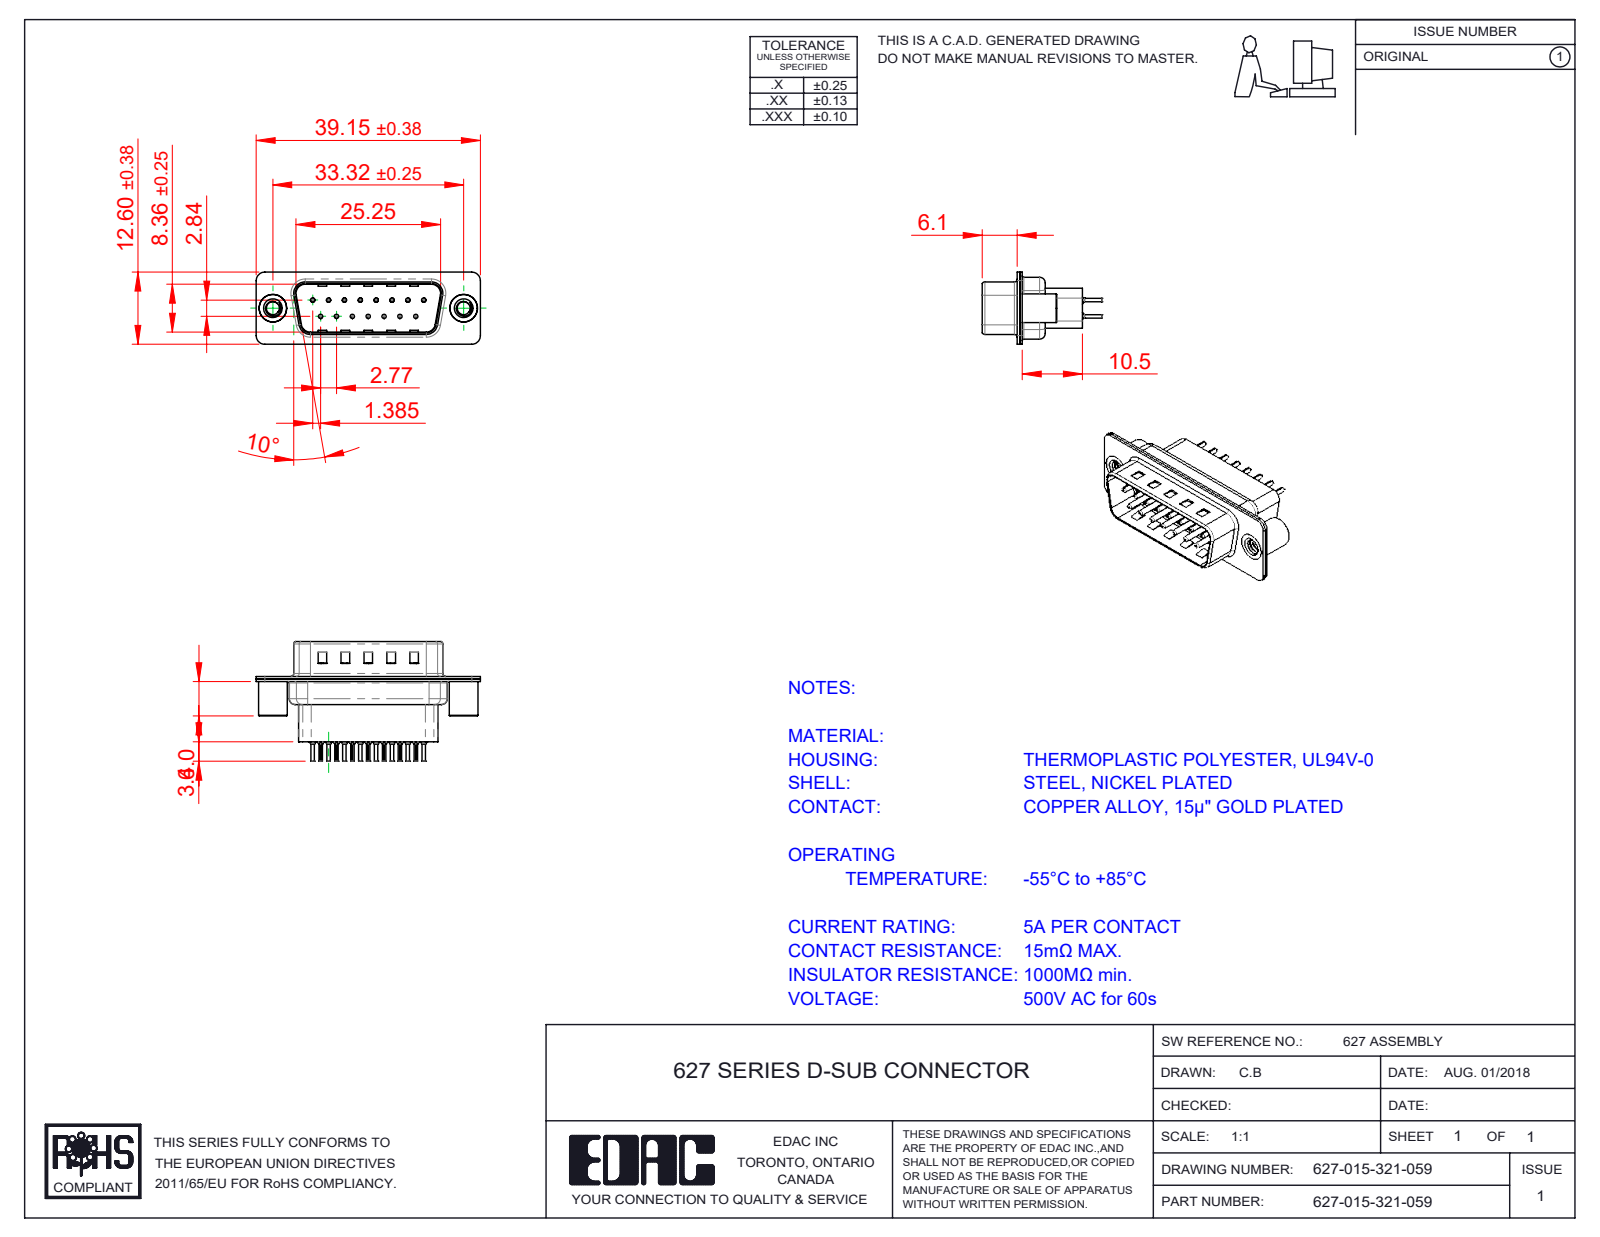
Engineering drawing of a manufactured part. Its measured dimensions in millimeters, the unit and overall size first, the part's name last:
Units: millimetres
Overall size (bounding box): 39.15 × 20.8 × 12.6
Round holes (diameter × count): ⌀0.2 ×15, ⌀0.35 ×15, ⌀1.1 ×15, ⌀1.6 ×15, ⌀2.26 ×2, ⌀4 ×2, ⌀4.8 ×2
Round bosses / shafts (diameter × count): ⌀2 ×15, ⌀1.5 ×15, ⌀0.75 ×15, ⌀0.6 ×15, ⌀5 ×2, ⌀4.9 ×2
Partial cylindrical surfaces — rounded edges, fillets, slot ends (radius × count): R0.1 ×30, R1.5 ×16, R2 ×12, R0.5 ×8, R1.6 ×8, R0.25 ×4, R0.6 ×4, R0.65 ×4
Main face-to-face distances: 0.4, 0.45, 0.9, 0.82, 9.58, 1.5, 0.68, 7.68, 1.4, 1.08
Hole centre spacings: 3.16, 2.77, 5.54, 8.31, 11.08, 5.03, 5.04, 7.48
Volume: 2 635 mm³ · Surface area: 6 801 mm²
Bodies: 20 solids, 1832 faces (499 planar, 708 cylindrical, 625 other)
Part name (STEP PRODUCT): 627 4-40 Threaded Standoff BS; 627 Contact Row 1_21H; 627 Shell Front_15 Contacts; 627 Shell Rear_15 Contacts (+3 more)
STEP written by: SolidWorks 2020 (CONFIG_CONTROL_DESIGN)
